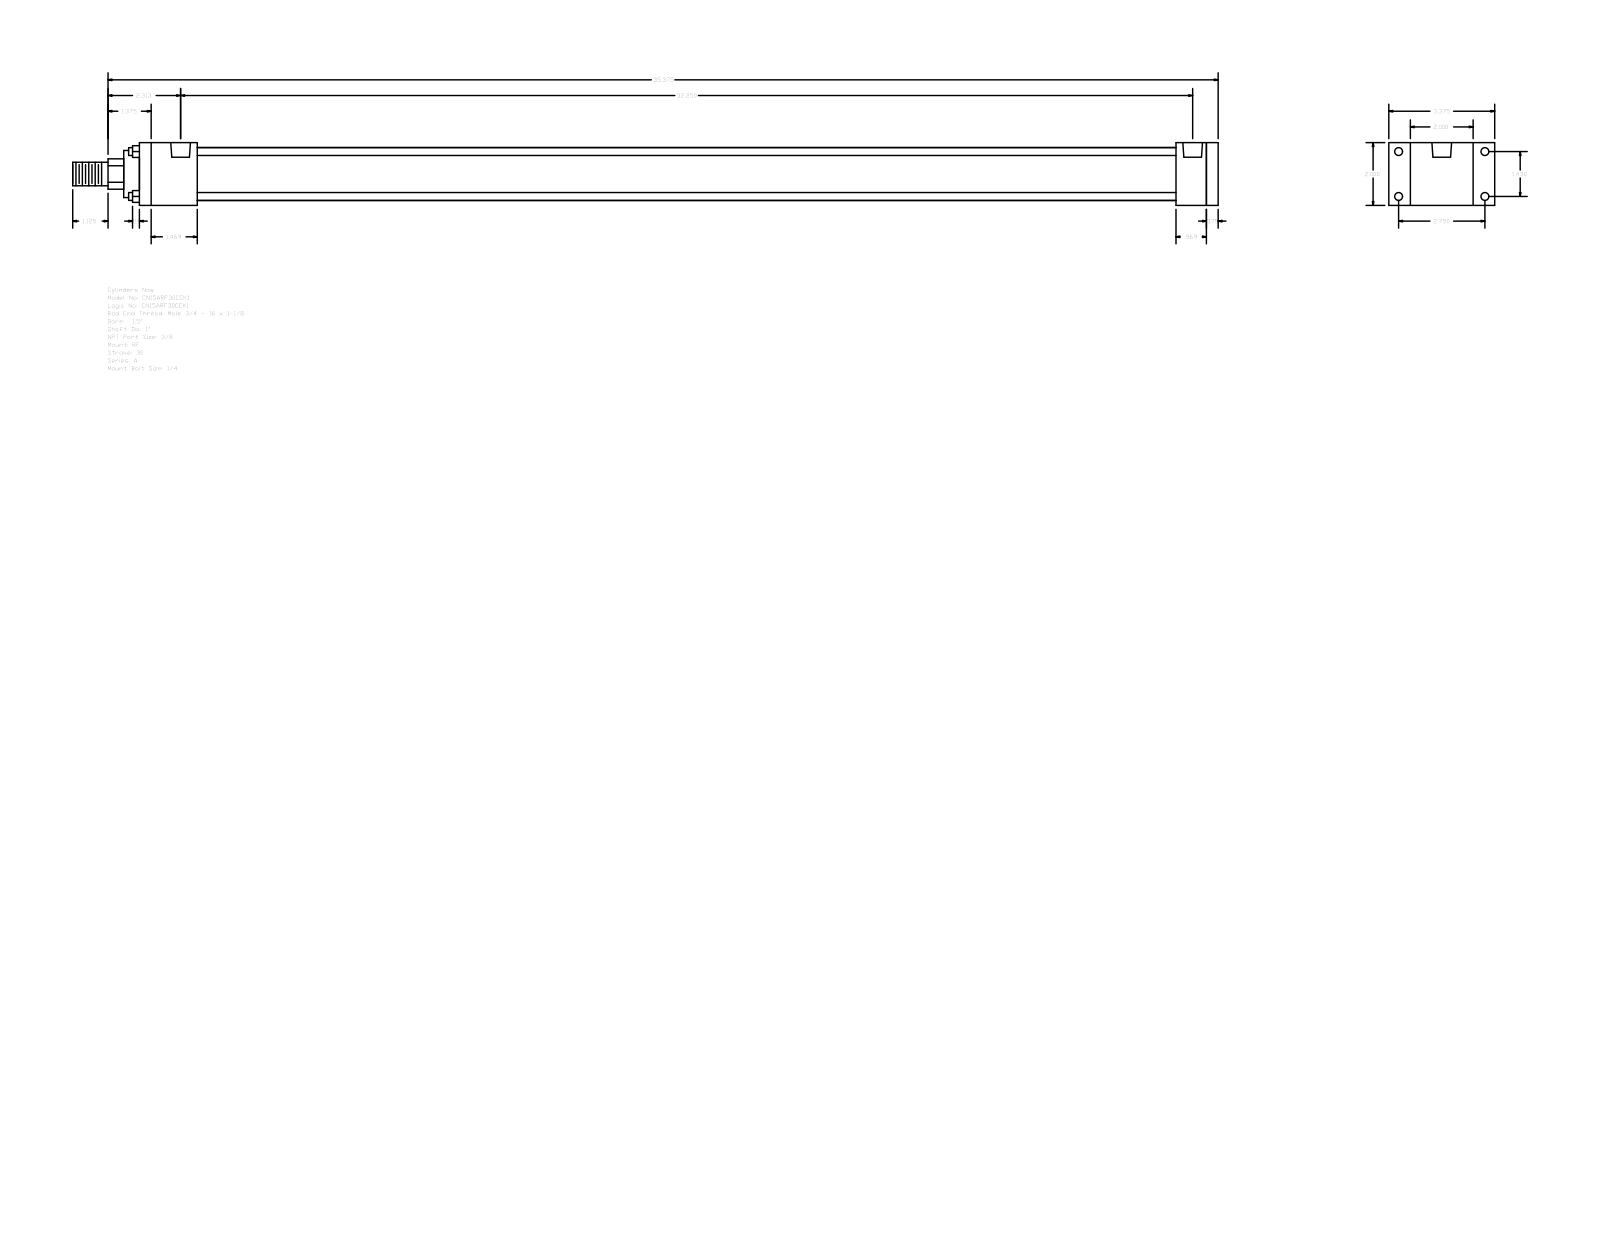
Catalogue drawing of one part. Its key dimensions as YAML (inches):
part_name: "A_RF__0150_1"
step_written_by: "GSSL Pune (CONFIG_CONTROL_DESIGN)"
units: inches
bodies: {solids: 0, faces: 92, planar: 64, cylindrical: 28, other: 0}
overall_size: [36.5, 3.375, 2]
round_holes:
  - {diameter: 0.219, count: 4}
  - {diameter: 0.25, count: 4}
  - {diameter: 0.627, count: 2}
round_bosses_or_shafts:
  - {diameter: 0.25, count: 4}
  - {diameter: 1.69, count: 1}
  - {diameter: 1.5, count: 1}
  - {diameter: 1, count: 1}
  - {diameter: 0.75, count: 1}
partial_cylinders:
  - {radius: 0.484, count: 1}
face_to_face_distances: [2, 0.375, 34, 34.375, 33.031, 0.969, 1.344, 1.844, 31.187, 32.156]
hole_center_spacings: [0.156, 1.43, 2.75, 3.099, 31.937, 32.094, 32.25]
